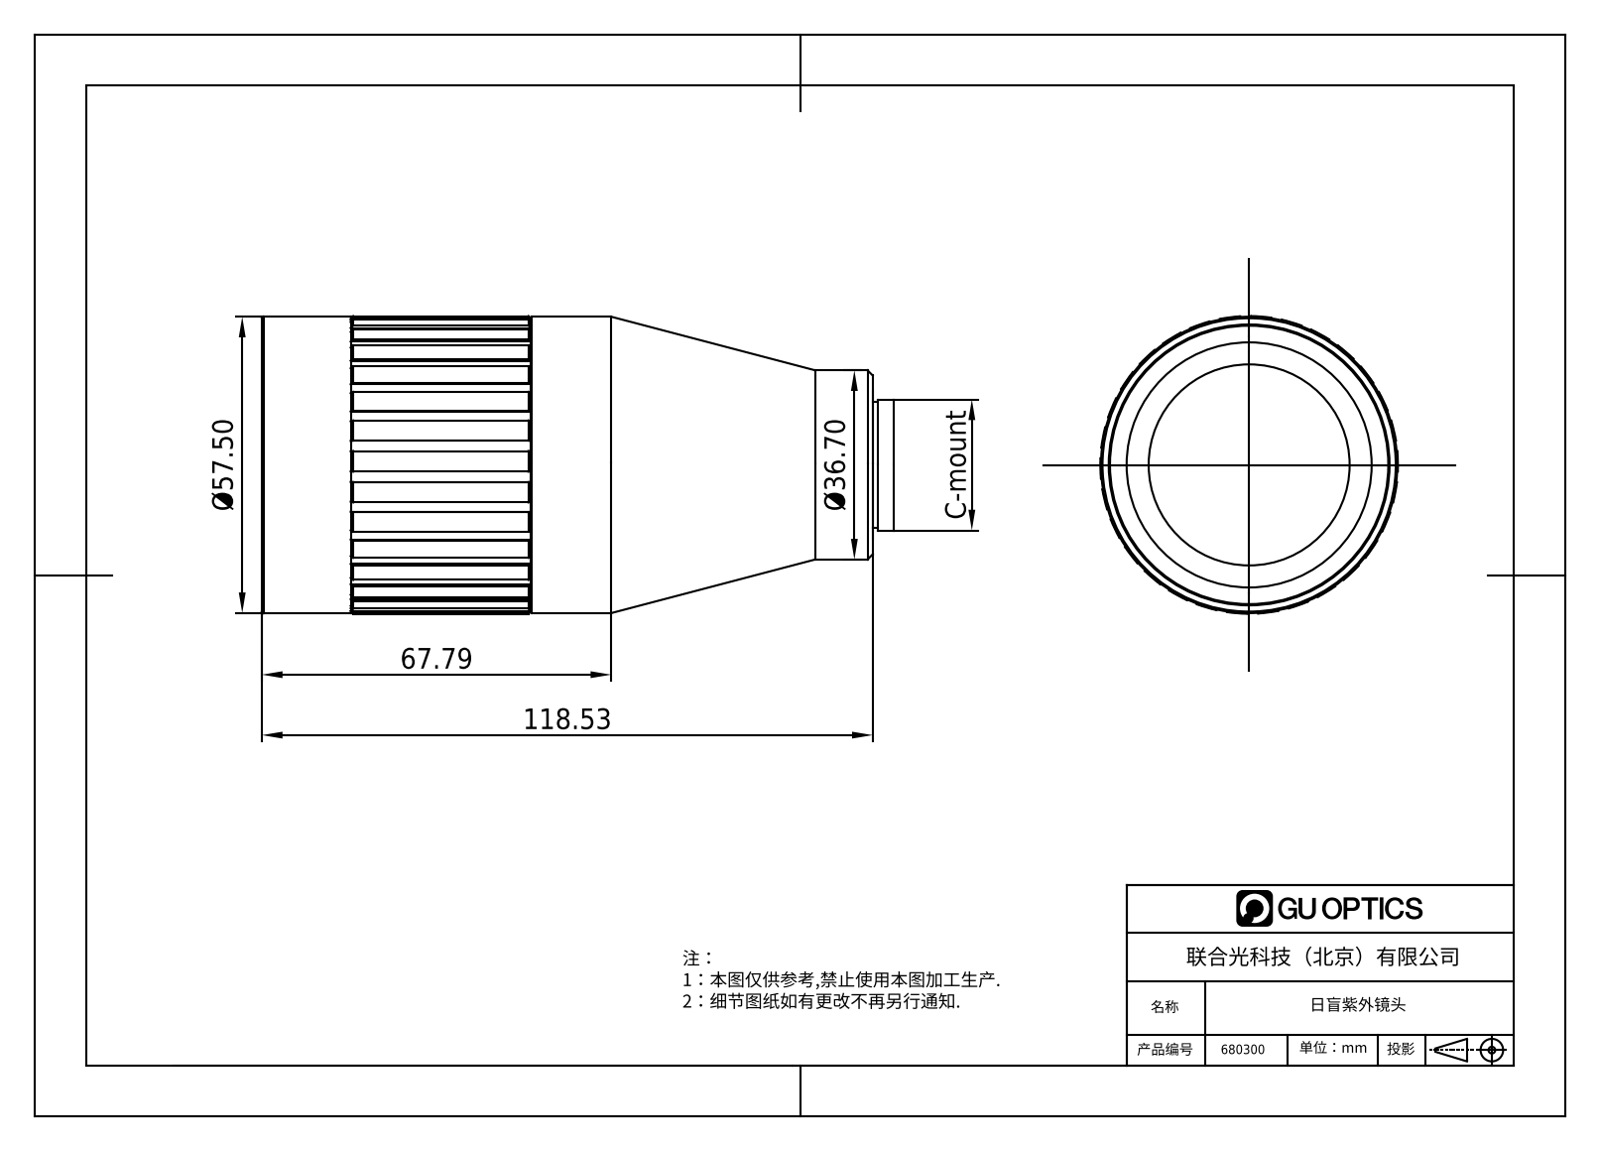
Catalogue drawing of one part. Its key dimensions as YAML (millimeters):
part_name: "紫外镜头"
step_written_by: "SolidWorks 2020 (CONFIG_CONTROL_DESIGN)"
units: millimeters
bodies: {solids: 13, faces: 155, planar: 46, cylindrical: 88, other: 21}
overall_size: [122.63, 58.21, 58.14]
volume: 135192
surface_area: 110862
round_holes:
  - {diameter: 2.05, count: 1}
  - {diameter: 22.4, count: 1}
  - {diameter: 27, count: 1}
  - {diameter: 31, count: 1}
  - {diameter: 32.1, count: 1}
  - {diameter: 33, count: 1}
  - {diameter: 36, count: 1}
  - {diameter: 38, count: 1}
  - {diameter: 39, count: 1}
  - {diameter: 40, count: 1}
  - {diameter: 48.1, count: 1}
  - {diameter: 51, count: 1}
round_bosses_or_shafts:
  - {diameter: 57.5, count: 1}
  - {diameter: 54, count: 1}
  - {diameter: 51.1, count: 1}
  - {diameter: 50, count: 1}
  - {diameter: 48, count: 1}
  - {diameter: 46, count: 1}
  - {diameter: 42, count: 1}
  - {diameter: 36.7, count: 1}
partial_cylinders:
  - {radius: 10.5, count: 21}
  - {radius: 29.12, count: 1}
face_to_face_distances: [8.51, 39.22, 71.59, 1.37, 7.14, 73.87, 72.5, 65.36, 6.28, 4.91]
